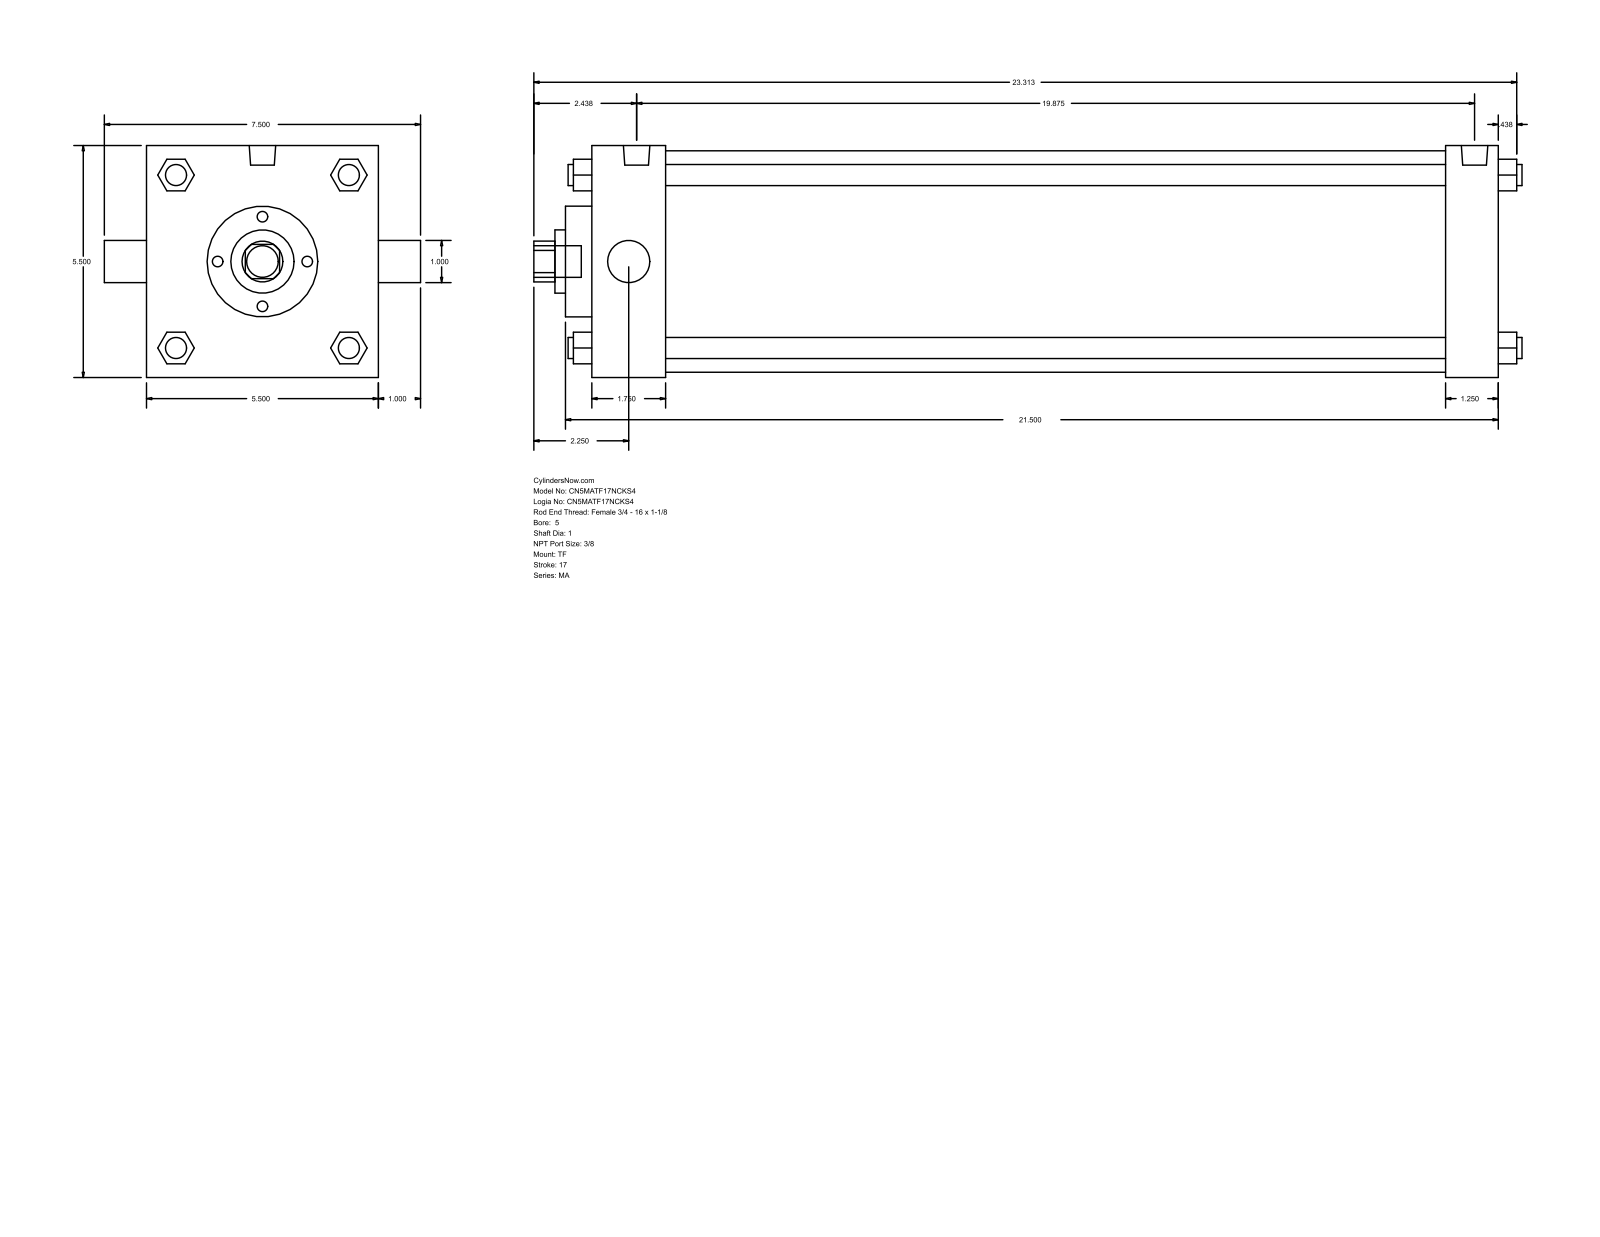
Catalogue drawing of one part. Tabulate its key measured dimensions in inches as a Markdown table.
| quantity | value |
| --- | --- |
| part name | MA_TF__0500_1 |
| STEP written by | GSSL Pune (CONFIG_CONTROL_DESIGN) |
| units | inches |
| bodies | 0 solids, 122 faces (93 planar, 29 cylindrical, 0 other) |
| overall size | 23.437 × 7.5 × 5.5 |
| round holes (diameter × count) | 1 × 2, 1.5 × 1, 2.625 × 1, 5.25 × 1 |
| round bosses / shafts (diameter × count) | 0.5 × 4, 0.437 × 3, 0.627 × 2, 0.75 × 1 |
| partial cylindrical surfaces (radius × count) | 0.484 × 1 |
| main face-to-face distances | 5.5, 21.5, 20.25, 1.25, 1.75, 18.5, 19.75, 0.625, 2.375, 20.875 |
